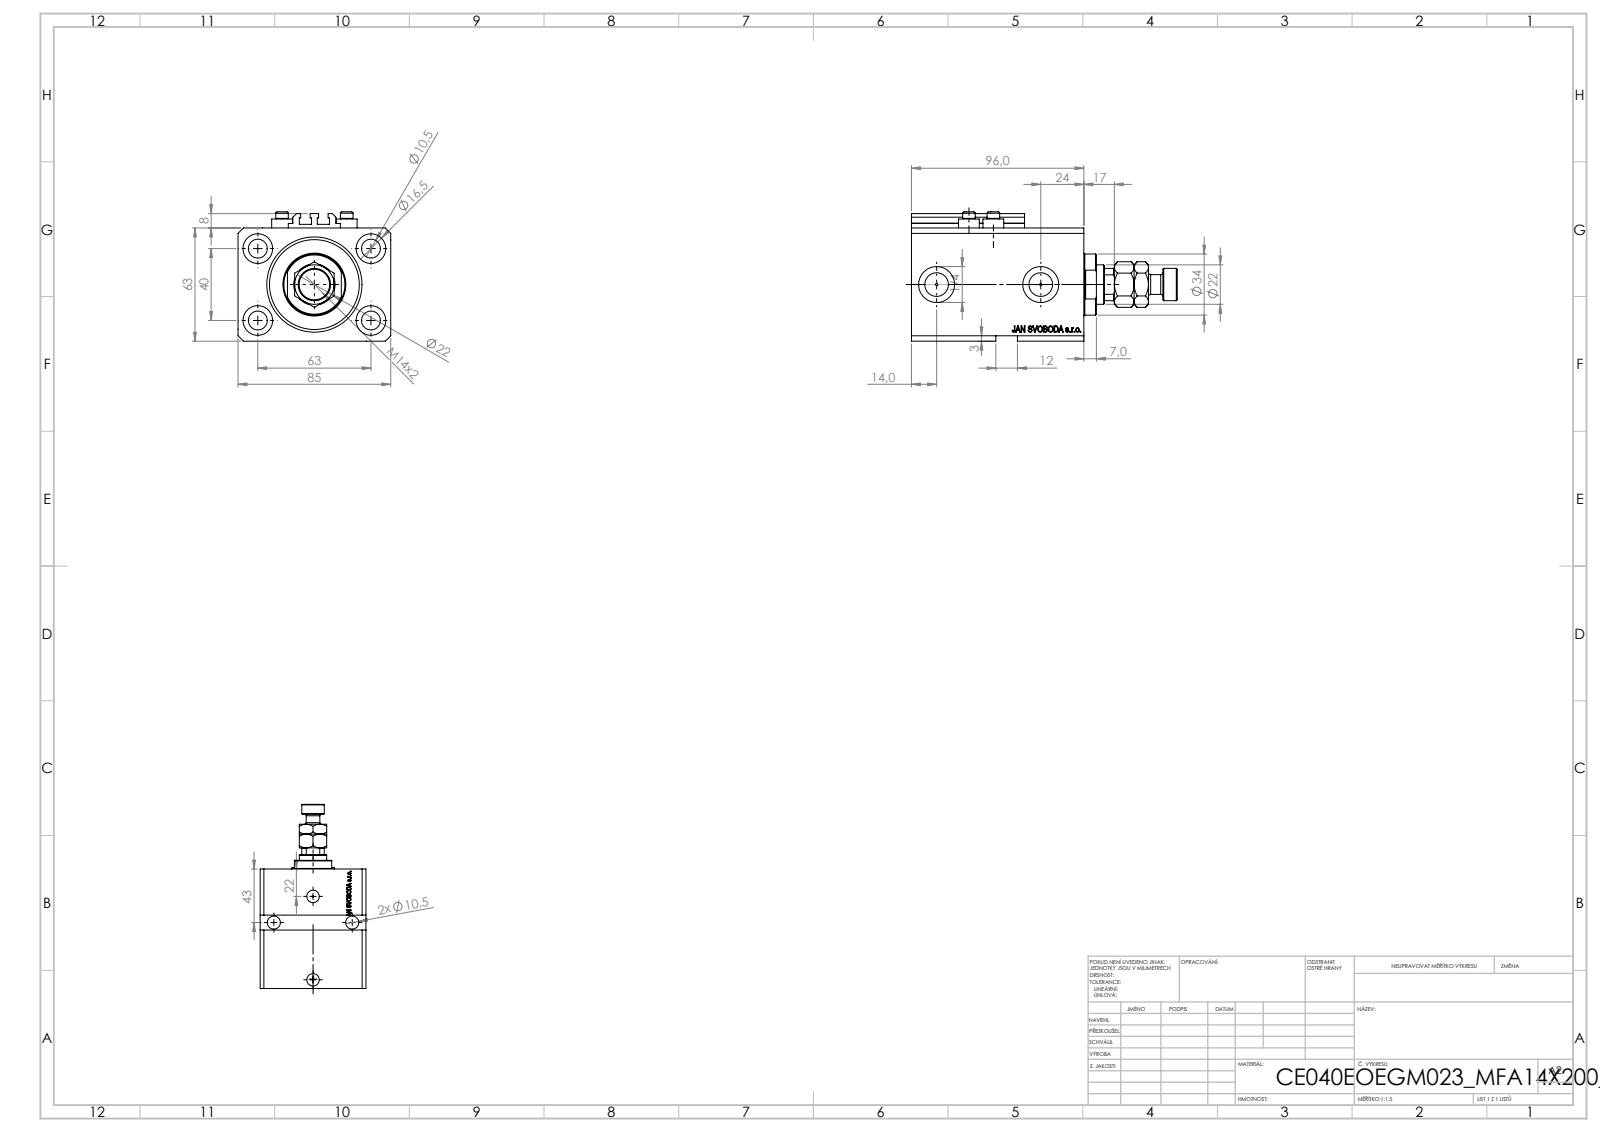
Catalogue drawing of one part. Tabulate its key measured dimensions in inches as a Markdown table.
| quantity | value |
| --- | --- |
| part name | ALLEN BOLT V250CE; V250CE_C_VCP; MFA; V250CE_VC_E (+1 more) |
| STEP written by | SolidWorks 2019 (CONFIG_CONTROL_DESIGN) |
| units | inches |
| bodies | 9 solids, 1139 faces (551 planar, 130 cylindrical, 458 other) |
| overall size | 5.827 × 3.346 × 2.835 |
| volume | 28.11 in³ |
| surface area | 156.8 in² |
| round holes (diameter × count) | 0.413 × 6, 0.049 × 4, 0.157 × 4, 0.65 × 4, 0.394 × 2, 0.518 × 2, 0.787 × 2, 0.492 × 1, 0.866 × 1, 1.575 × 1, 2.087 × 1 |
| round bosses / shafts (diameter × count) | 0.457 × 4, 0.276 × 4, 1.339 × 1, 0.709 × 1, 0.433 × 1 |
| partial cylindrical surfaces (radius × count) | 0.008 × 10, 0.413 × 1 |
| main face-to-face distances | 2.48, 3.346, 0.669, 3.78, 3.11, 0.449, 2.661, 3.331, 0.118, 2.677 |
| hole center spacings | 1.469, 2.48, 0.535, 0.606, 0.983, 1.196, 1.213, 1.324 |
